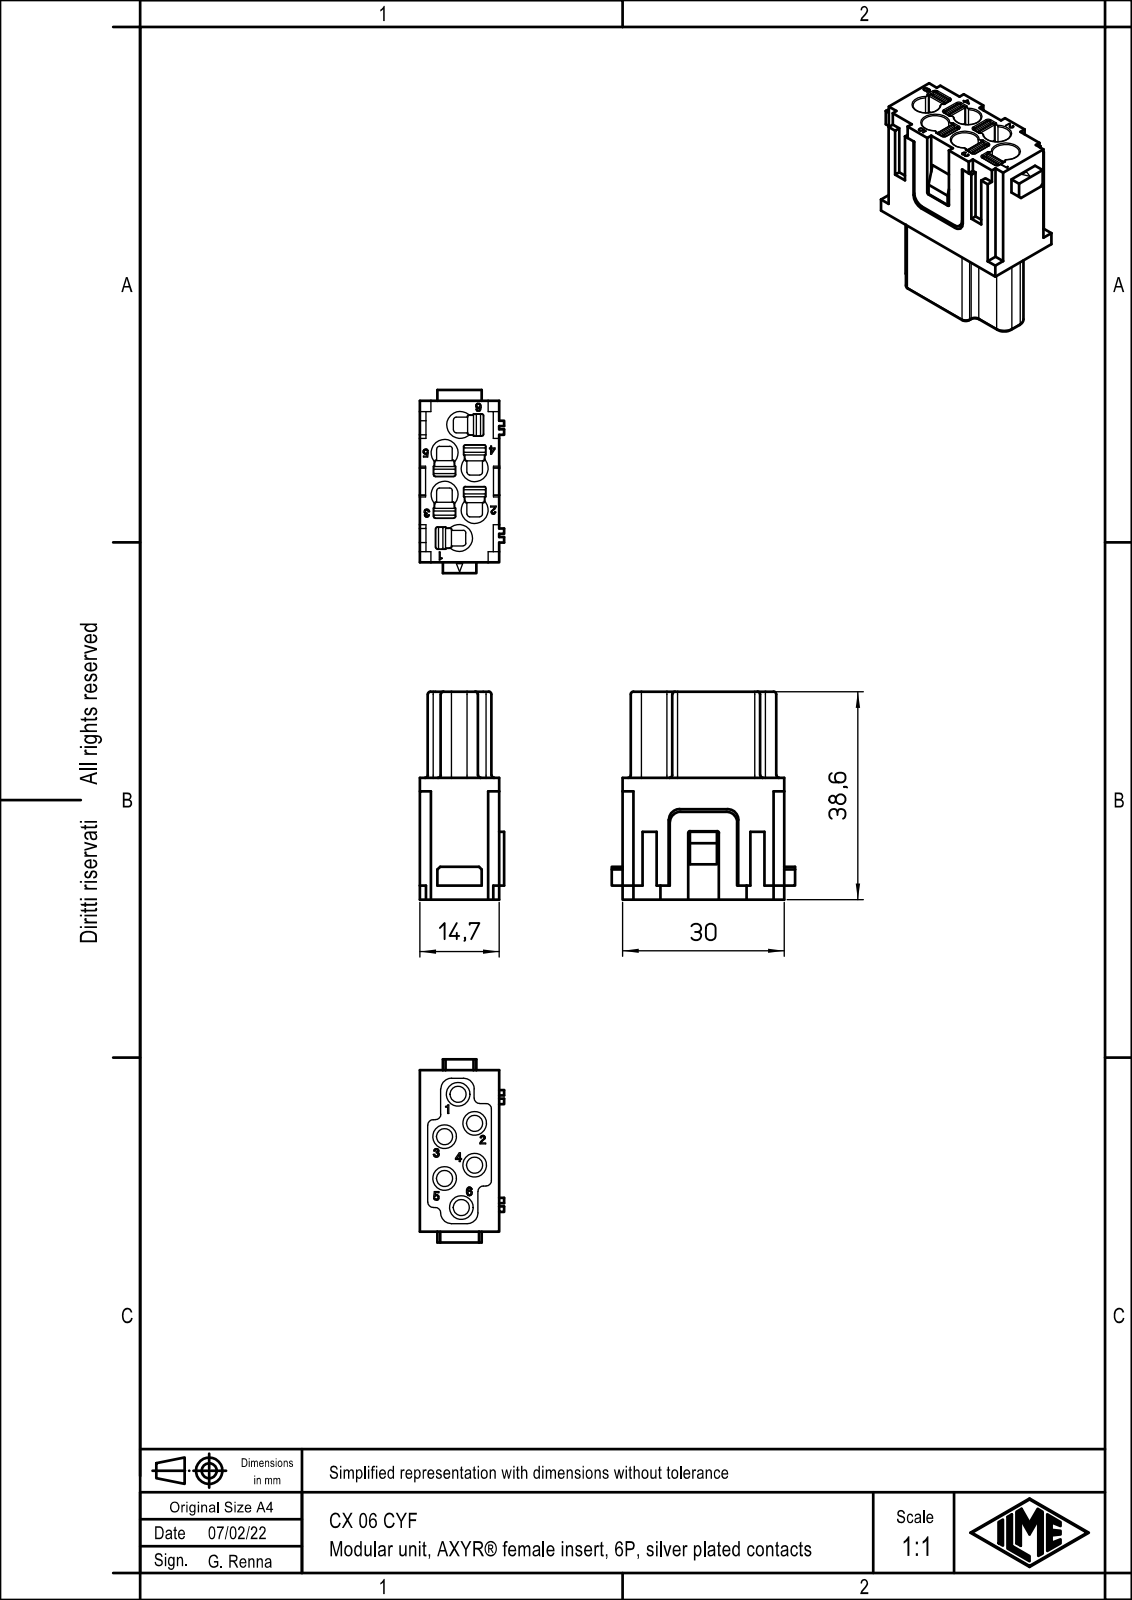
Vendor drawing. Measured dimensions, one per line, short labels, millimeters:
name: CX_06_CYF
written by: Creo Elements/Direct Modeling 20.1B 02-Apr-2019 (C) Parametric Technology GmbH (AUTOMOTIVE_DESIGN)
unit: mm
bodies: 1 solid, 928 faces (600 planar, 244 cylindrical, 84 other)
size: 38.6 × 34 × 15.6
volume: 12 371 mm³; area: 6 255 mm²
holes: 6× ⌀3, 6× ⌀4.4
rounds: 64× R0.2, 36× R0.4, 34× R0.5, 14× R0.3, 14× R2, 12× R0.1, 8× R1, 6× R2.5
face distances: 14.7, 1.45, 13.25, 0.6, 30, 2, 11.8, 16, 1.8, 1.9
hole spacings: 6.11, 6.23, 7.75, 8.24, 13.51, 15.8, 7.71, 11.64
